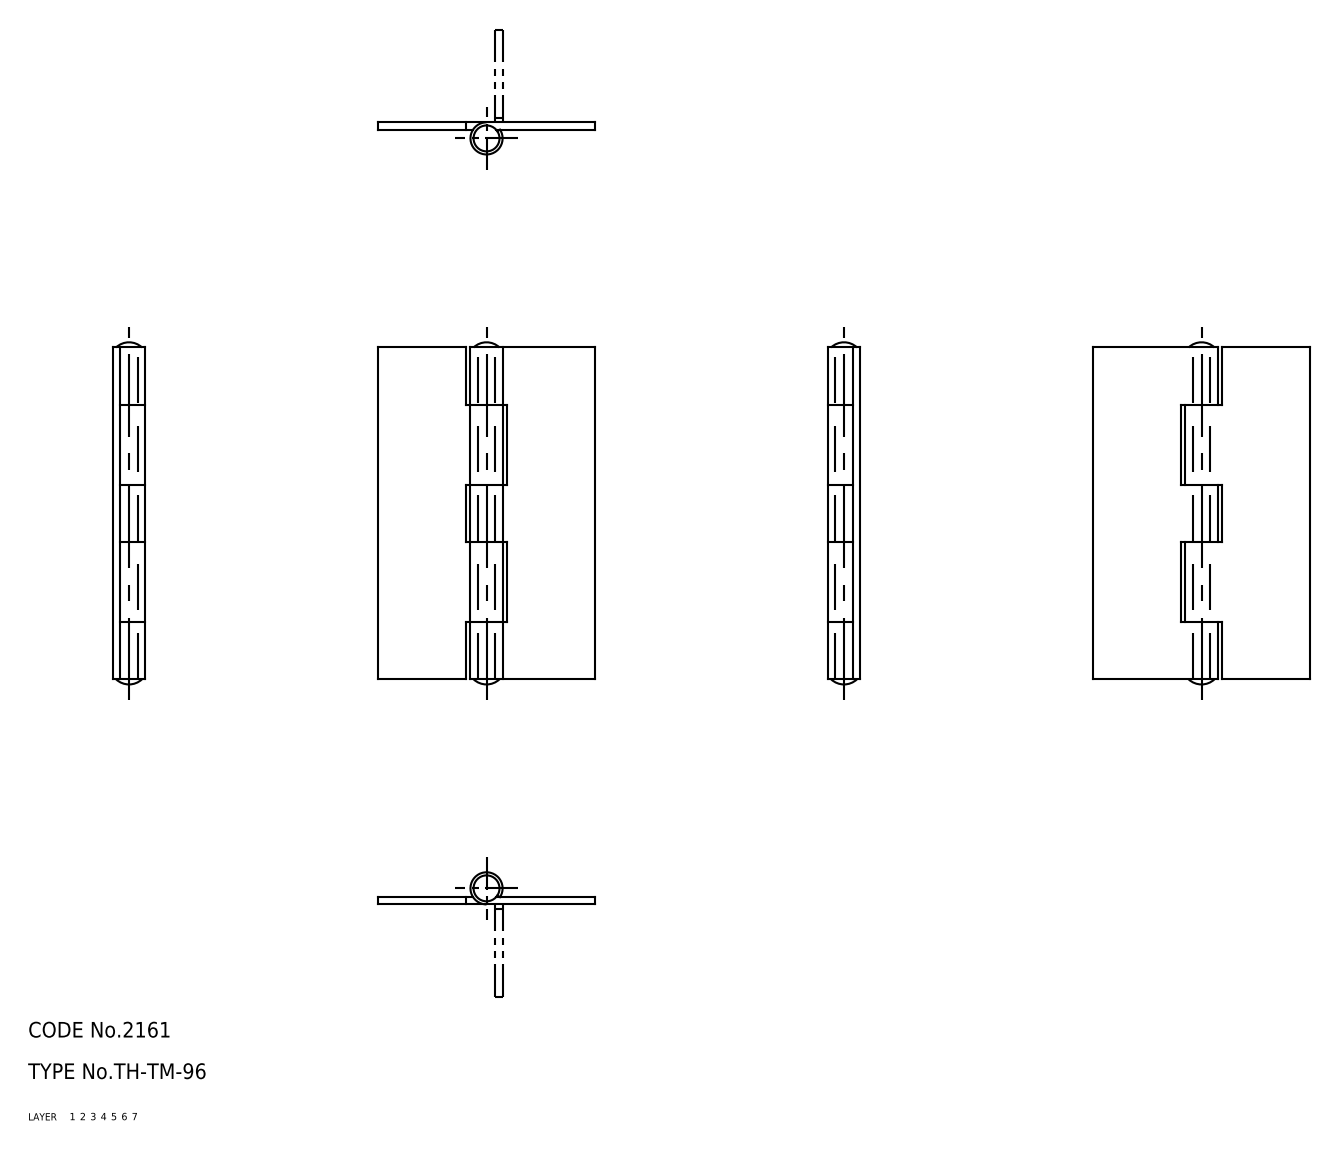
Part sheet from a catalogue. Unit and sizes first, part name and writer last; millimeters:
Units: millimetres
Overall size (bounding box): 66 × 42 × 6.2
Volume: 5 142 mm³ · Surface area: 7 922 mm²
Bodies: 3 solids, 44 faces (0 planar, 0 cylindrical, 44 other)
Part name (STEP PRODUCT): 67111014; 67111027; 67111040
STEP written by: CADfix (AUTOMOTIVE_DESIGN)
